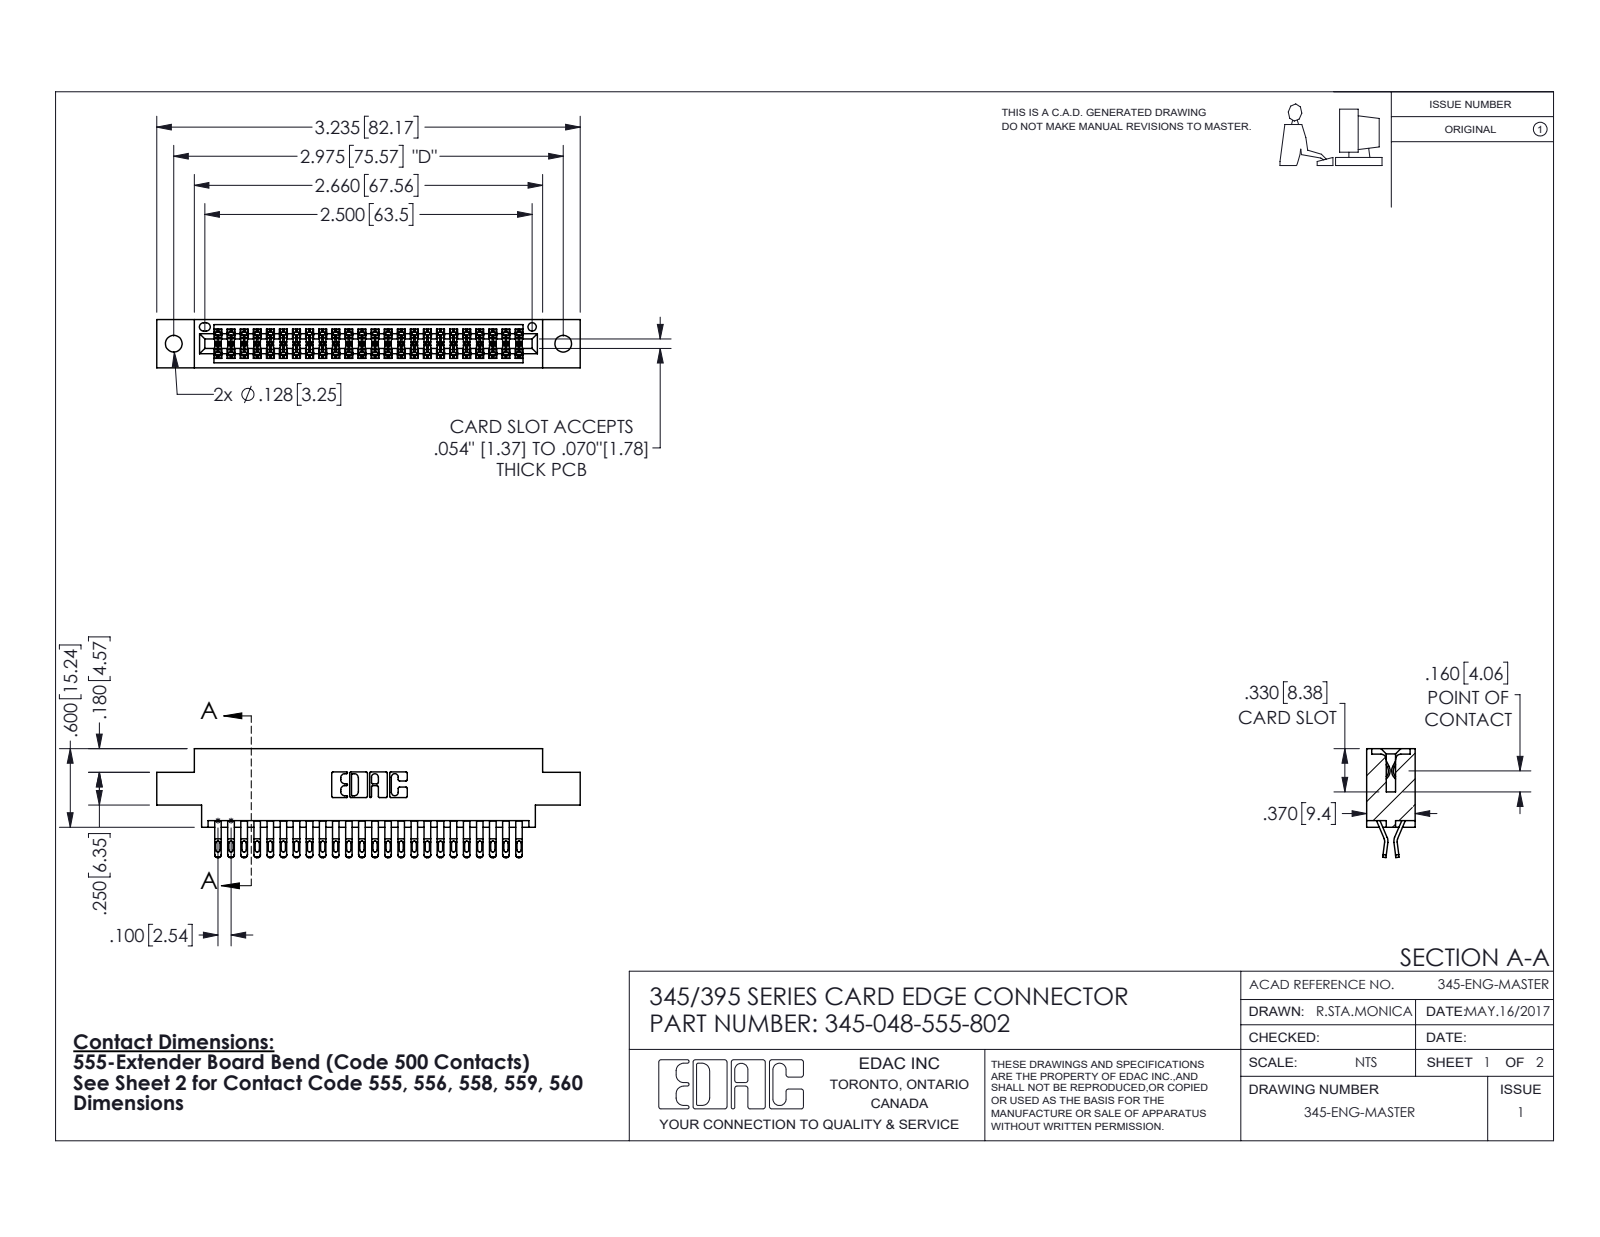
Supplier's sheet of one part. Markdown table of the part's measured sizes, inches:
| quantity | value |
| --- | --- |
| part name | 345 Part_0.170 Offset - 0.128 Dia; 345-292-001_555 Tail; 345-048-555-802 |
| STEP written by | SolidWorks 2016 (CONFIG_CONTROL_DESIGN) |
| units | inches |
| bodies | 49 solids, 2818 faces (1572 planar, 1246 cylindrical, 0 other) |
| overall size | 3.235 × 0.832 × 0.37 |
| volume | 0.476 in³ |
| surface area | 17.89 in² |
| round holes (diameter × count) | 0.128 × 2, 0.064 × 1 |
| partial cylindrical surfaces (radius × count) | 0.016 × 120, 0.02 × 96, 0.006 × 72, 0.01 × 22, 0.007 × 6, 0.031 × 6, 0.026 × 3, 0.01 × 2 |
| main face-to-face distances | 0.298, 0.072, 0.37, 0.2, 0.025, 0.098, 0.272, 0.225, 0.175, 0.15 |
| hole center spacings | 0.27, 2.741, 2.975 |
